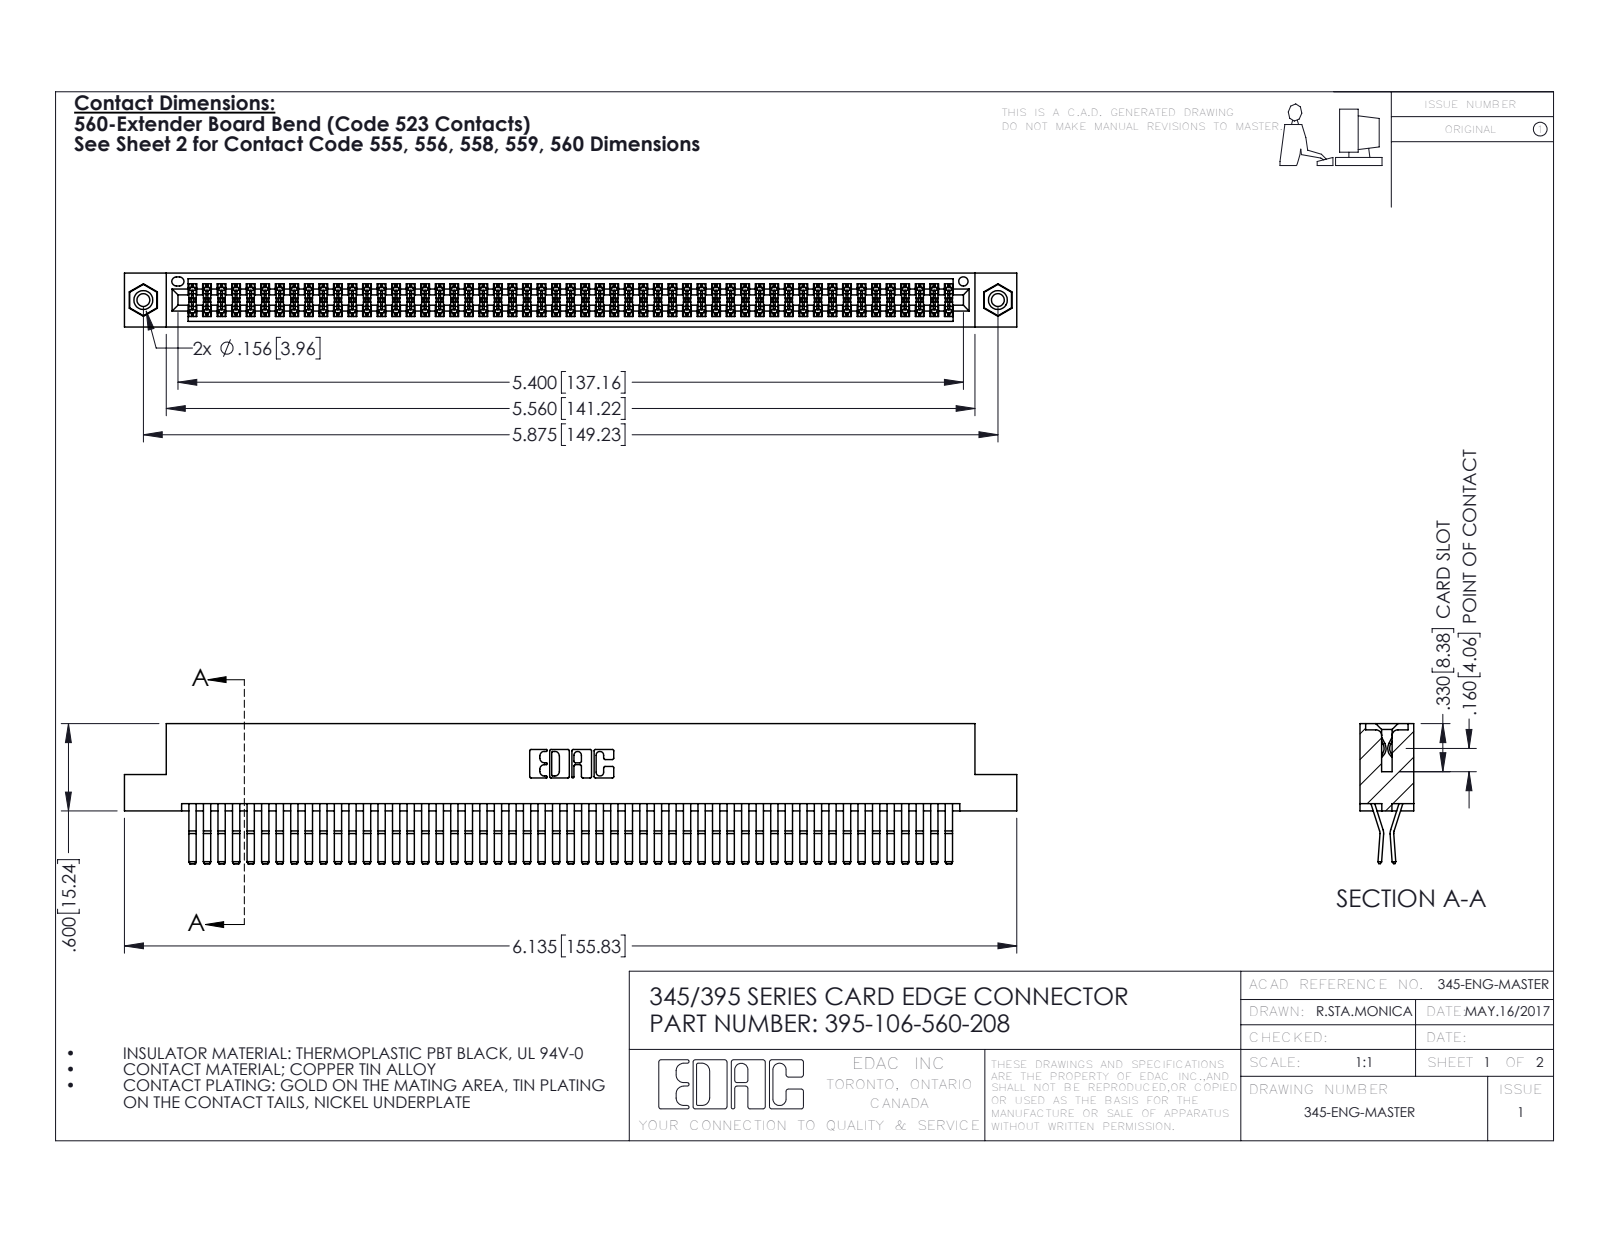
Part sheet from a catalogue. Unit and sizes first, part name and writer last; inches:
Units: inches
Overall size (bounding box): 6.135 × 0.962 × 0.37
Round holes (diameter × count): ⌀0.089 ×2, ⌀0.125 ×2, ⌀0.156 ×2, ⌀0.064 ×1
Round bosses / shafts (diameter × count): ⌀0.155 ×2
Partial cylindrical surfaces — rounded edges, fillets, slot ends (radius × count): R0.006 ×160, R0.01 ×22, R0.007 ×6, R0.031 ×6, R0.026 ×3, R0.01 ×2, R0.014 ×2, R0.019 ×2
Main face-to-face distances: 0.025, 0.072, 0.298, 0.37, 0.2, 0.098, 0.272, 0.225, 0.175, 0.149
Hole centre spacings: 0.27, 5.639, 5.875
Volume: 0.972 in³ · Surface area: 39.61 in²
Bodies: 109 solids, 5698 faces (3610 planar, 2072 cylindrical, 16 other)
Part name (STEP PRODUCT): 345 Part_Flush Mounting Lugs - 0.156 Dia-TI; 345-292-001_560 Tail; 345-250-001_345-250-003-102; 395-106-560-208
STEP written by: SolidWorks 2016 (CONFIG_CONTROL_DESIGN)
